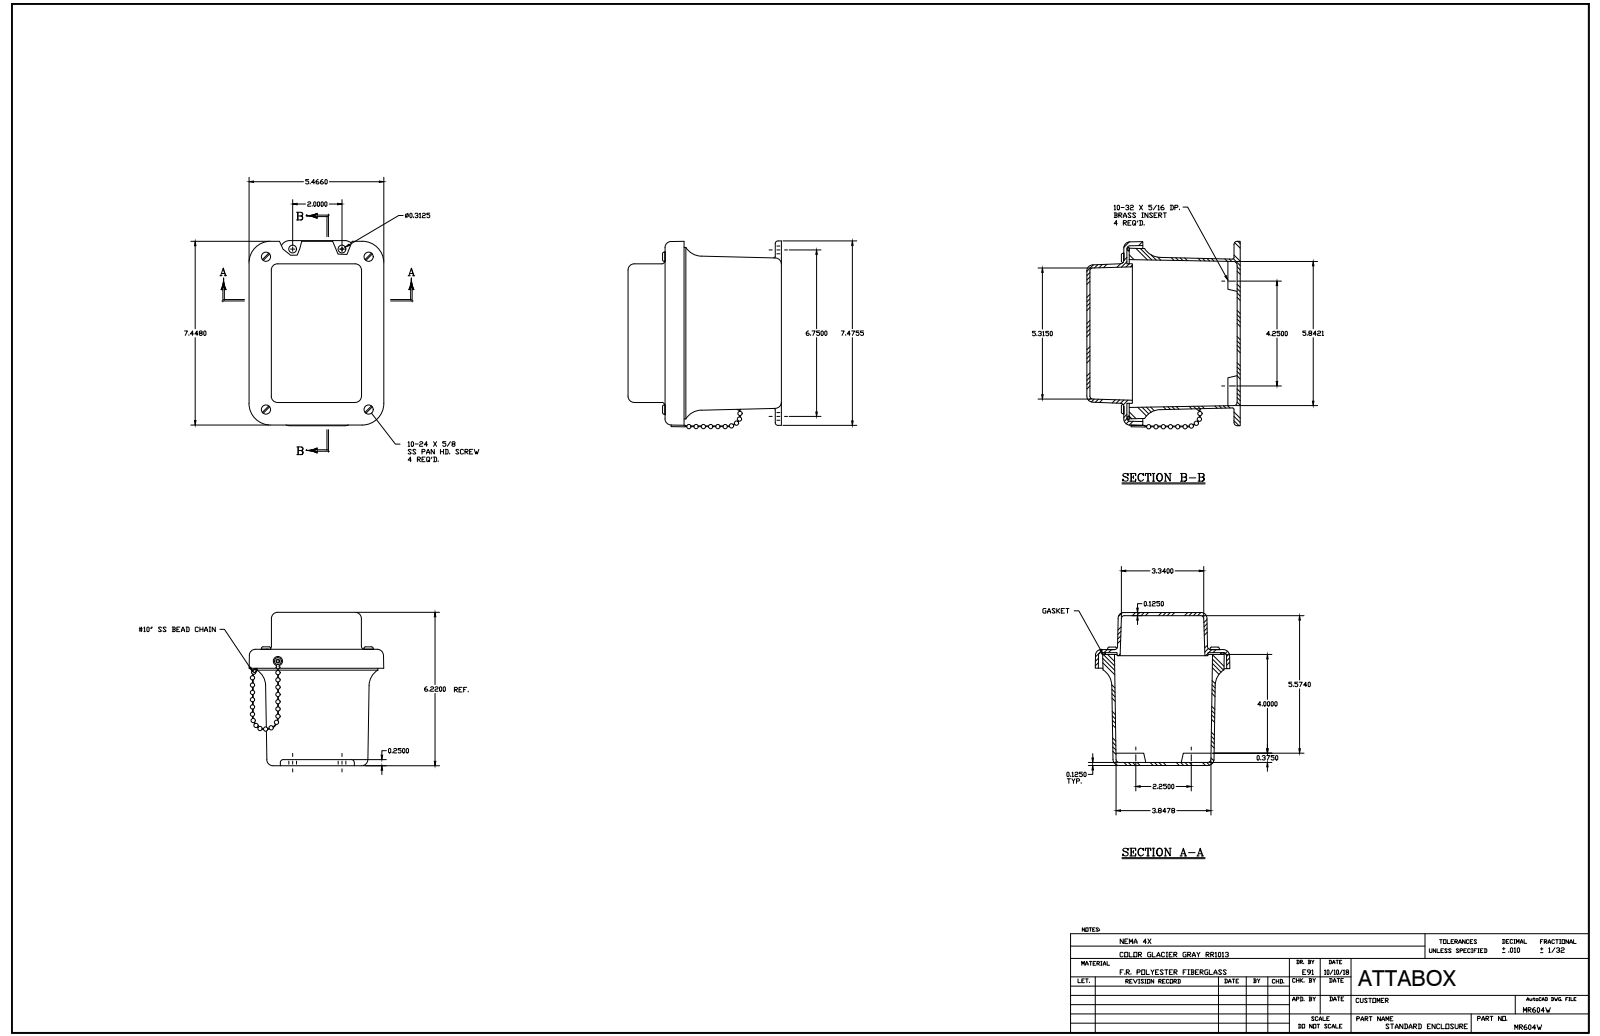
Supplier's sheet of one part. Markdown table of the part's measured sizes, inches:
| quantity | value |
| --- | --- |
| part name | MR604W |
| STEP written by | SolidWorks 2018 (AUTOMOTIVE_DESIGN) |
| units | inches |
| bodies | 47 solids, 939 faces (208 planar, 297 cylindrical, 434 other) |
| overall size | 8 × 6.213 × 5.721 |
| volume | 33.18 in³ |
| surface area | 433.8 in² |
| round holes (diameter × count) | 0.152 × 5, 0.145 × 4, 0.156 × 4, 0.218 × 4, 0.14 × 3, 0.187 × 2, 0.126 × 1 |
| round bosses / shafts (diameter × count) | 0.27 × 8, 0.19 × 4, 0.156 × 4, 0.375 × 2, 0.25 × 2, 0.283 × 1, 0.125 × 1, 0.125 × 1 |
| partial cylindrical surfaces (radius × count) | 0.031 × 20, 0.125 × 20, 0.25 × 12, 0.2 × 4, 0.309 × 4, 0.313 × 4, 0.375 × 4, 0.75 × 4 |
| main face-to-face distances | 0.125, 0.125, 1.5, 4.463, 4.588, 5.963, 6.088, 6.213, 1.625, 6.088 |
| hole center spacings | 3.339, 1.341, 2.25, 4.156, 4.25, 4.808, 5.28, 6.102 |
